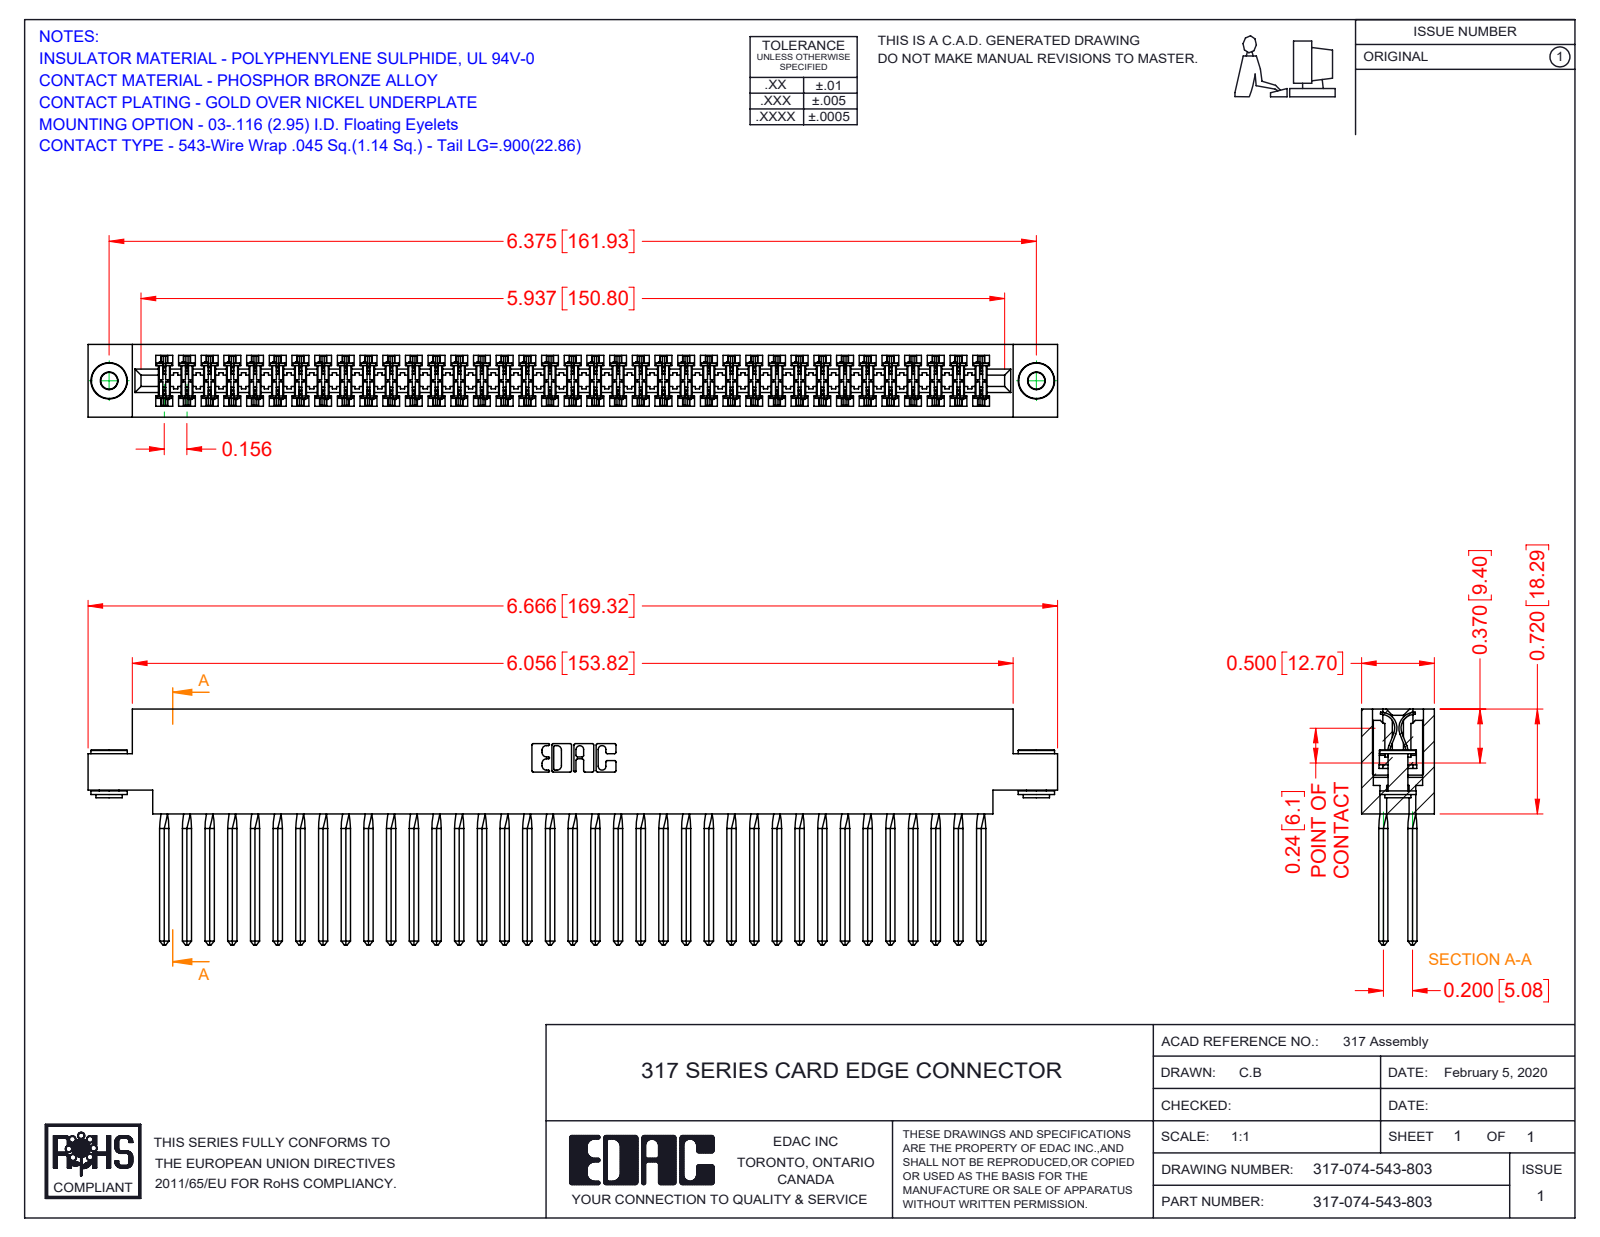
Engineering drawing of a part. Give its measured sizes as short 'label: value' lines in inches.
name: 317-290-001_543; 317-074-543-803; 317 Part_.156 Dia - TH; 345-250-002_345-250-002-102
written by: SolidWorks 2016 (CONFIG_CONTROL_DESIGN)
unit: in
bodies: 77 solids, 6726 faces (5470 planar, 952 cylindrical, 304 other)
size: 6.666 × 1.62 × 0.5
volume: 1.747 in³; area: 67.36 in²
holes: 2× ⌀0.116, 2× ⌀0.156
bosses: 2× ⌀0.25, 2× ⌀0.18, 2× ⌀0.136
rounds: 148× R0.015, 22× R0.01, 6× R0.007, 6× R0.031, 3× R0.026, 2× R0.095, 2× R0.1, 2× R0.11
face distances: 0.5, 0.075, 0.425, 0.35, 0.11, 0.195, 0.094, 0.2, 0.115, 0.131
hole spacings: 6.375
